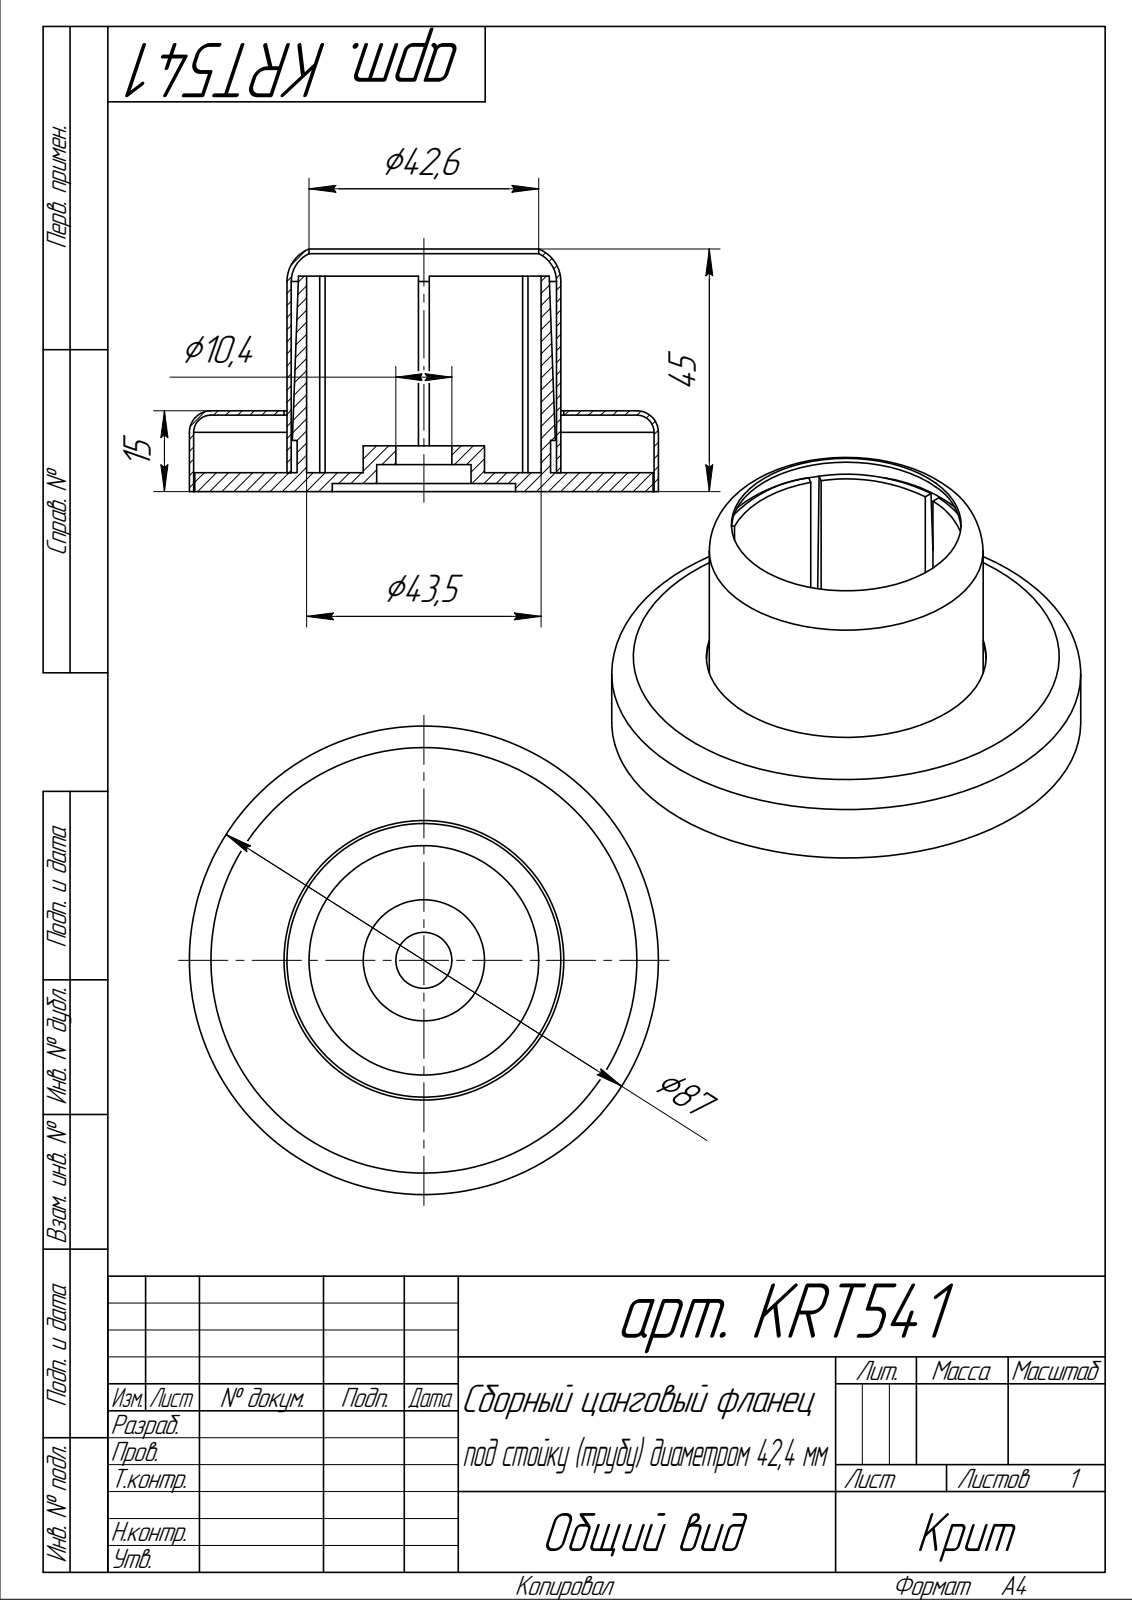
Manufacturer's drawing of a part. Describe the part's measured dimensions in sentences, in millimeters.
The part is named "арт. KRT541.002; арт. KRT541; арт. KRT541.001; арт. KRT541.003". Its 3-D file was written by "SolidWorks 2014 (AUTOMOTIVE_DESIGN)". It is 3 solids with 107 faces: 39 planar, 53 cylindrical and 15 other. Overall it measures 87 by 87 by 45.04 millimeters. Its volume is 37 771 cubic millimeters and its surface area 51 926 square millimeters. Round holes: 3 of diameter 6.5, 3 of diameter 8.5, 1 of diameter 10.4, 1 of diameter 17.5, 1 of diameter 42.6, 1 of diameter 43.5, 1 of diameter 49.2, 1 of diameter 51.9, 1 of diameter 85.4. Round bosses or shafts: 1 of diameter 87, 1 of diameter 85, 1 of diameter 50.8, 1 of diameter 47, 1 of diameter 22.5. Partial cylindrical surfaces (rounded edges, fillets, slot ends): 4 of radius 2, 1 of radius 26.5. The main face-to-face distances are 3.5, 14.2, 15, 10.7, 11.5, 0.8, 2, 1.5, 12.7, 13.5. The hole center spacings are 34.5, 59.76, 69.
